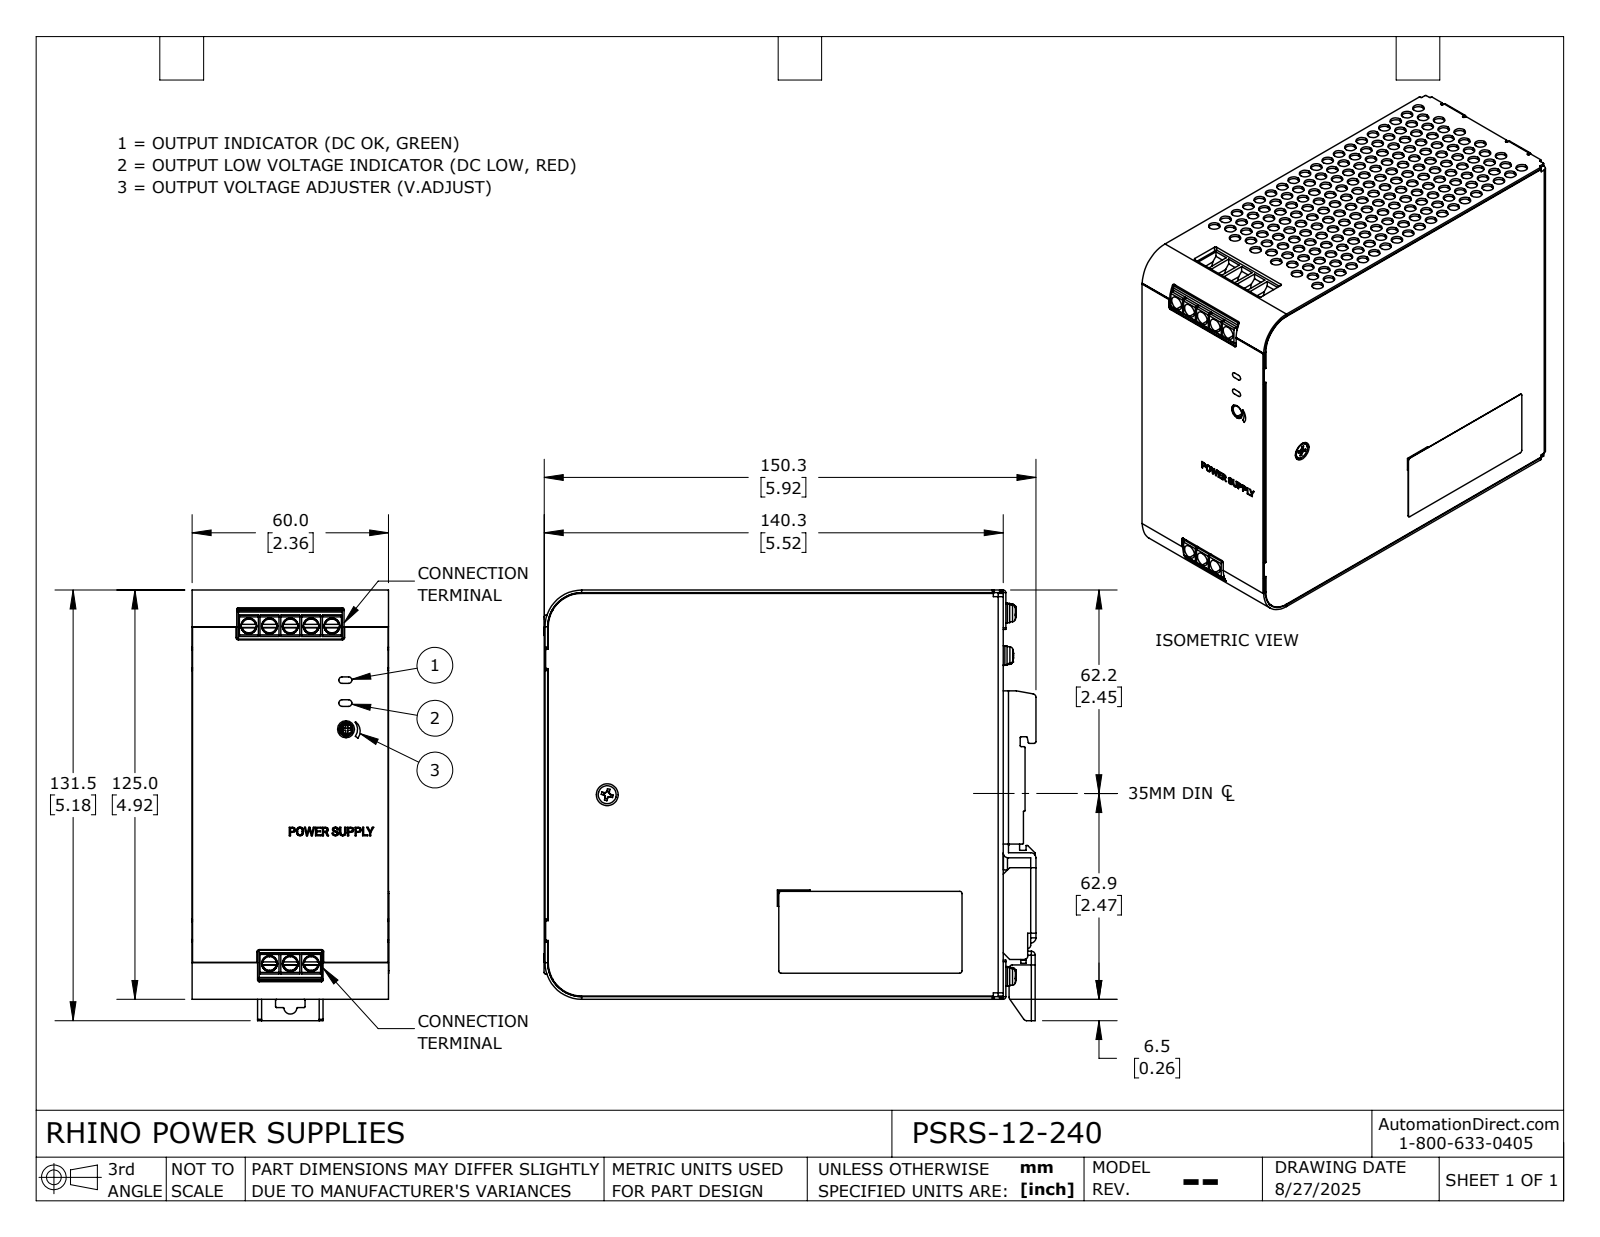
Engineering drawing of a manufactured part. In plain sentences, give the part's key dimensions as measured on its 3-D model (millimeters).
The part is named "PSRS-12-240". Its 3-D file was written by "SolidWorks 2024 (AUTOMOTIVE_DESIGN)". It is 2 solids with 3059 faces: 1489 planar, 1291 cylindrical and 279 other. Overall it measures 150.3 by 131.5 by 60.05 millimeters. Its volume is 1 048 000 cubic millimeters and its surface area 95 151 square millimeters. Round holes: 210 of diameter 4, 10 of diameter 3.1, 10 of diameter 3.5, 8 of diameter 4.65, 8 of diameter 4.85, 6 of diameter 3.8, 5 of diameter 3.6, 4 of diameter 2.5, 4 of diameter 6.7, 1 of diameter 1.5, 1 of diameter 3.4, 1 of diameter 4.2. Round bosses or shafts: 16 of diameter 3, 10 of diameter 6, 10 of diameter 5.9, 8 of diameter 4.75, 4 of diameter 5.5. Partial cylindrical surfaces (rounded edges, fillets, slot ends): 61 of radius 0.3, 37 of radius 0.5, 14 of radius 0.15, 14 of radius 1, 13 of radius 1.6, 9 of radius 1.2, 7 of radius 0.1, 2 of radius 0.6. The main face-to-face distances are 60, 0.8, 124.2, 140.25, 125, 1.6, 123.4, 8.4, 13.6, 1.2. The hole center spacings are 11.64, 5.6, 15.15, 11.2, 21.15, 19.65, 10.2, 23.27.
